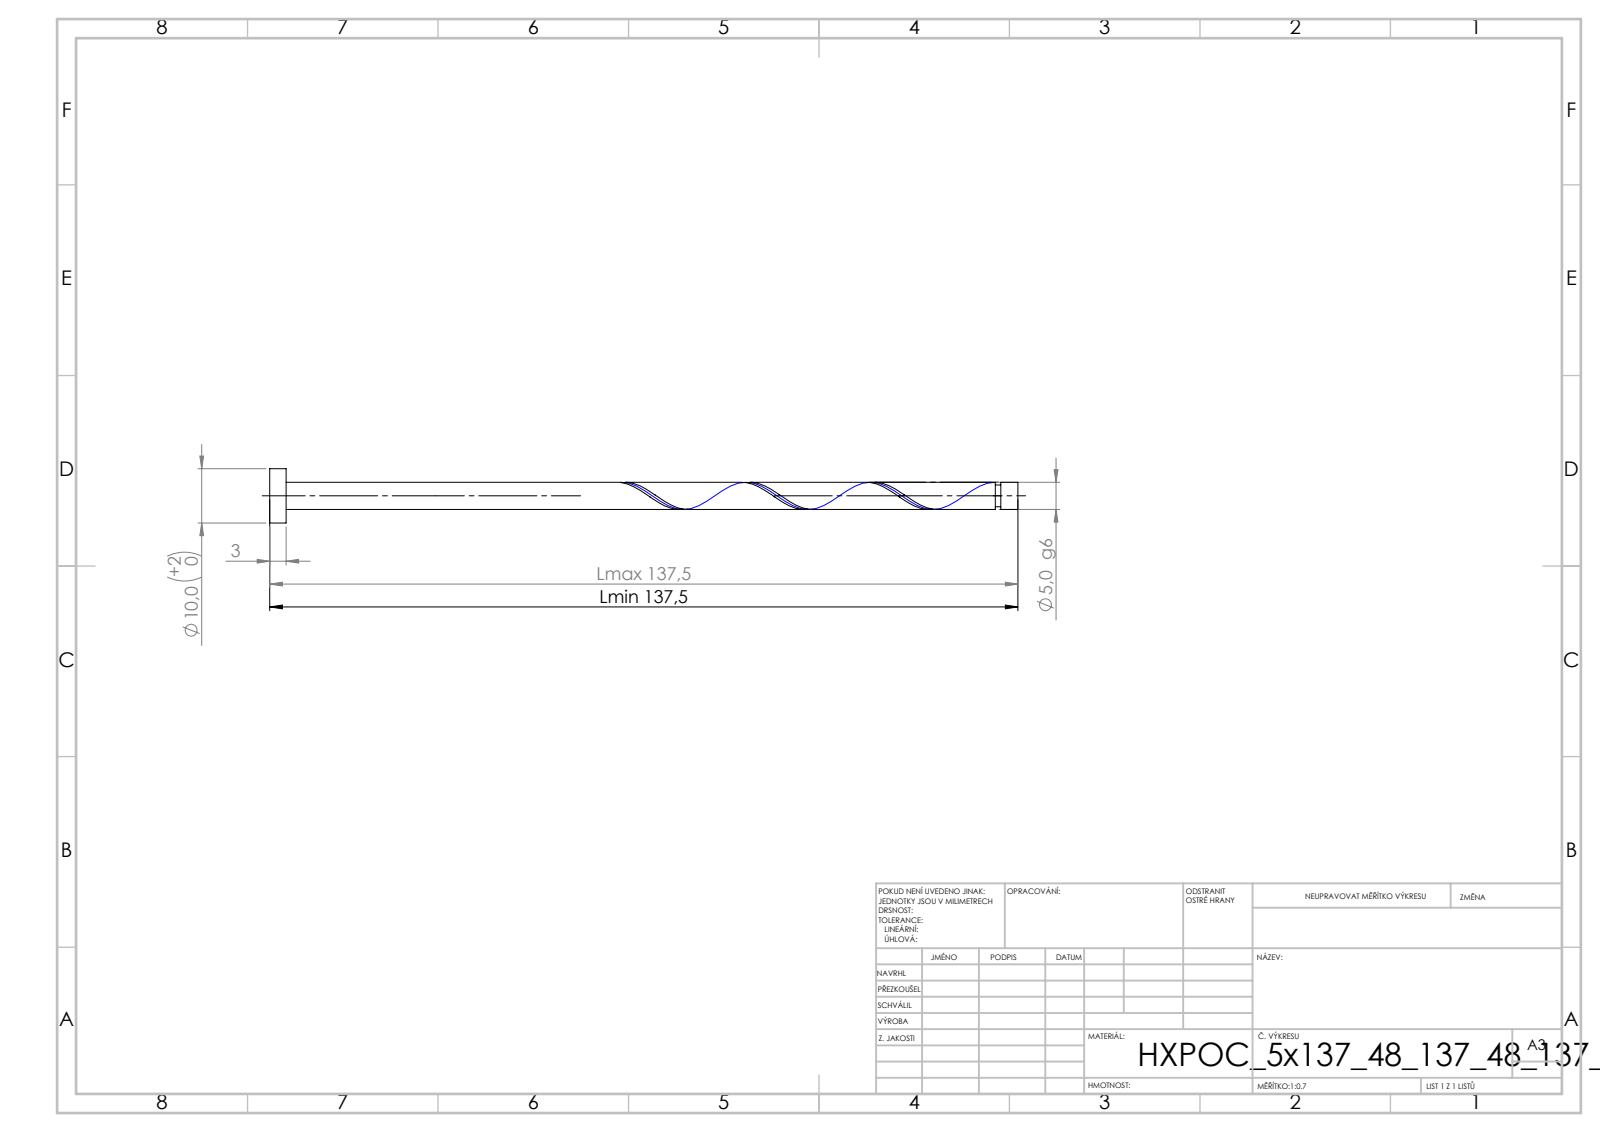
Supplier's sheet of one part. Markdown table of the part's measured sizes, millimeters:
| quantity | value |
| --- | --- |
| STEP written by | SolidWorks 2019 (CONFIG_CONTROL_DESIGN) |
| units | millimeters |
| bodies | 1 solid, 21 faces (6 planar, 14 cylindrical, 1 other) |
| overall size | 137.48 × 10 × 10 |
| volume | 2 843 mm³ |
| surface area | 2 417 mm² |
| round bosses / shafts (diameter × count) | 10 × 1, 5 × 1, 4 × 1 |
| main face-to-face distances | 3, 137.48, 134.48, 134.32, 131.32, 3.16, 133.32, 130.32, 1, 4.16 |
